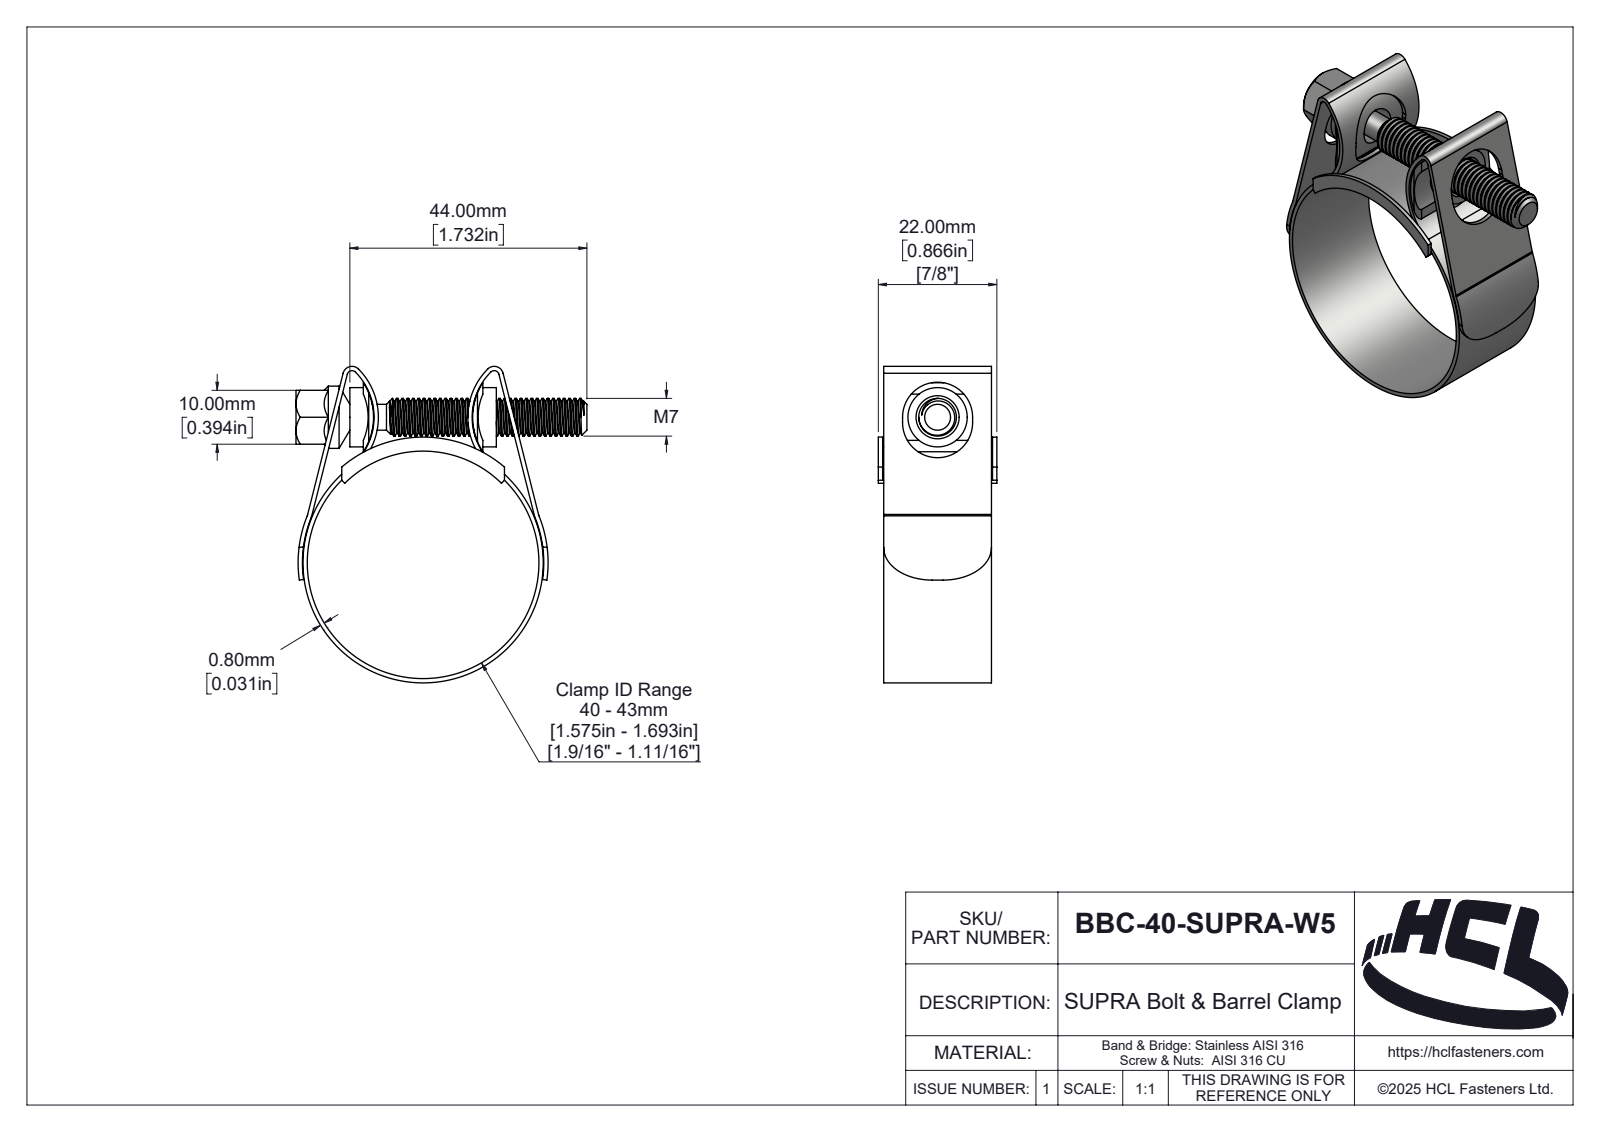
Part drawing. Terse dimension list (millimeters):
name: BBC-40-SUPRA-W5
written by: SolidWorks 2025 (AUTOMOTIVE_DESIGN)
unit: mm
bodies: 5 solids, 309 faces (46 planar, 184 cylindrical, 79 other)
size: 58.73 × 54 × 22
volume: 6 783 mm³; area: 13 479 mm²
holes: 1× ⌀43
bosses: 1× ⌀11.55, 1× ⌀11, 1× ⌀7, 1× ⌀4.8
rounds: 4× R1, 2× R0.9, 2× R1.7, 2× R2, 2× R2.8, 2× R6.5, 2× R10.78, 2× R11.78
face distances: 0.8, 20, 1, 21, 10, 21.2, 20.2, 2.5, 24.68, 22
